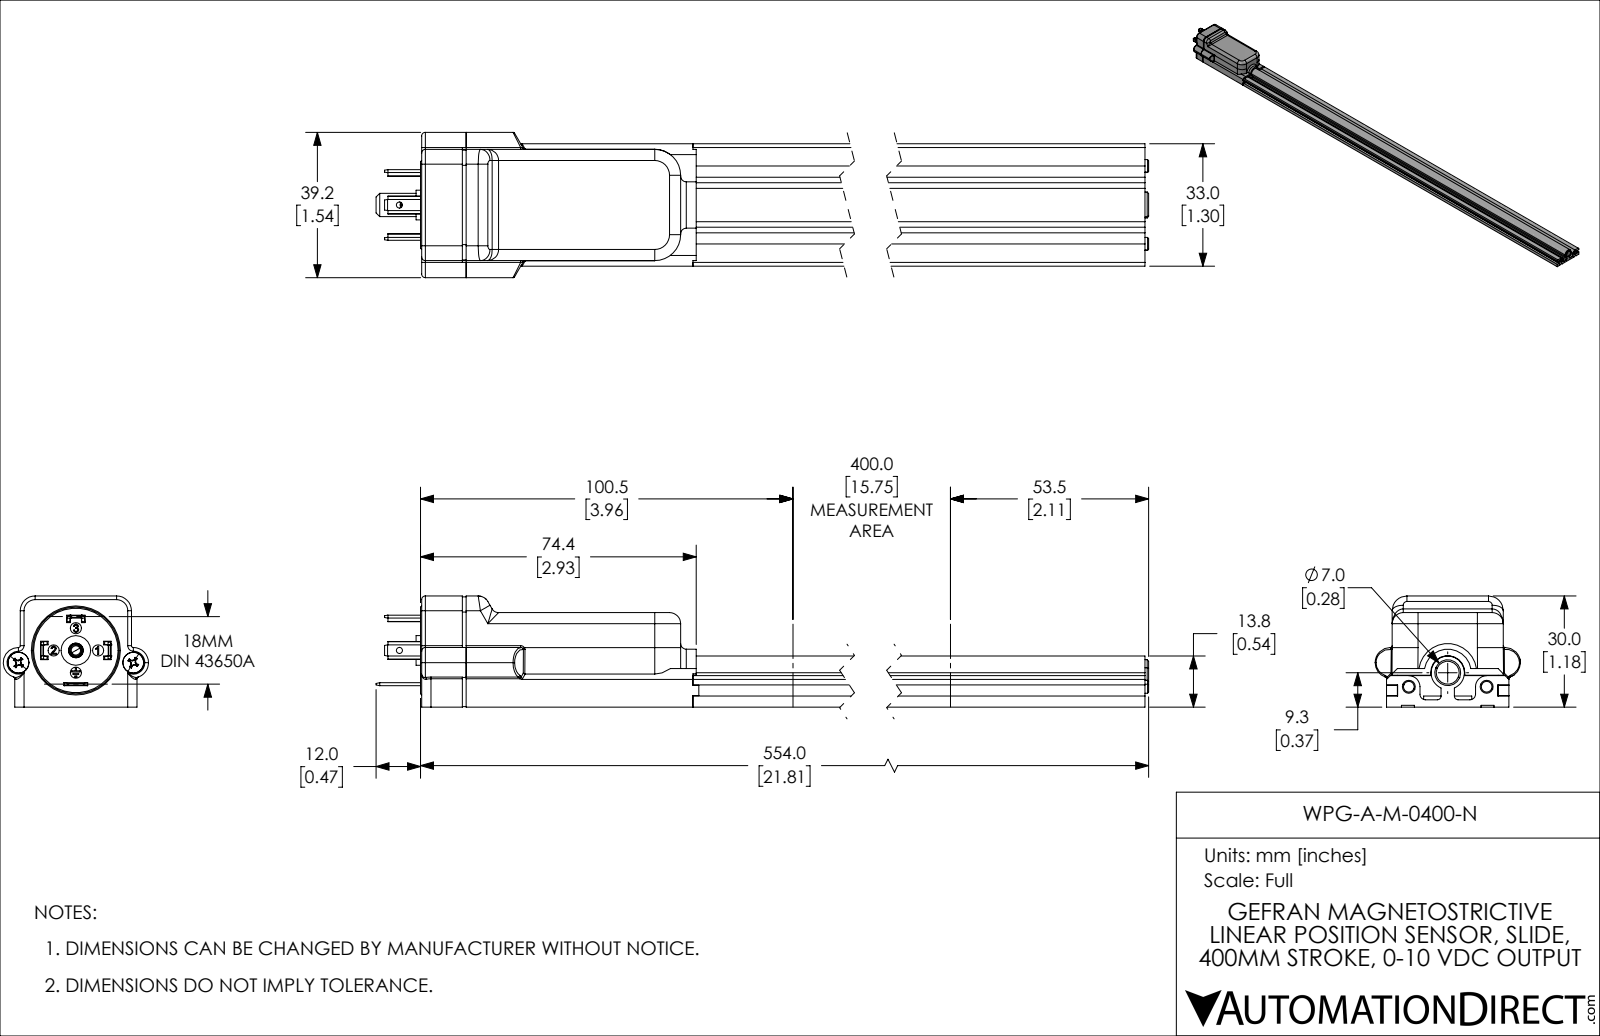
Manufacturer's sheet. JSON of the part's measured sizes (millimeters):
{"part_name": "WPG-A-M-0400-N", "step_written_by": "SolidWorks 2021 (CONFIG_CONTROL_DESIGN)", "units": "millimeters", "bodies": {"solids": 15, "faces": 589, "planar": 371, "cylindrical": 139, "other": 79}, "overall_size": [566, 39.2, 30], "volume_mm3": 171388, "surface_area_mm2": 80342, "round_holes": [[3, 5], [1.5, 2], [1.65, 2], [3.2, 2], [5.7, 2], [1.6, 1], [2.5, 1], [4, 1]], "round_bosses_or_shafts": [[5.6, 2], [3.5, 2], [2.85, 2], [9, 1], [8, 1], [7, 1], [5.3, 1], [3.94, 1]], "partial_cylinders_radius": [[0.5, 8], [3, 8], [0.85, 6], [1, 5], [0.8, 4], [1.5, 4], [4.1, 4], [7, 4]], "face_to_face_distances": [3, 2.5, 5.5, 1, 6, 1.5, 8.5, 30, 0.5, 8], "hole_center_spacings": [6, 8.49, 10.06, 12, 12.3, 15.73, 15.85, 18.08]}
